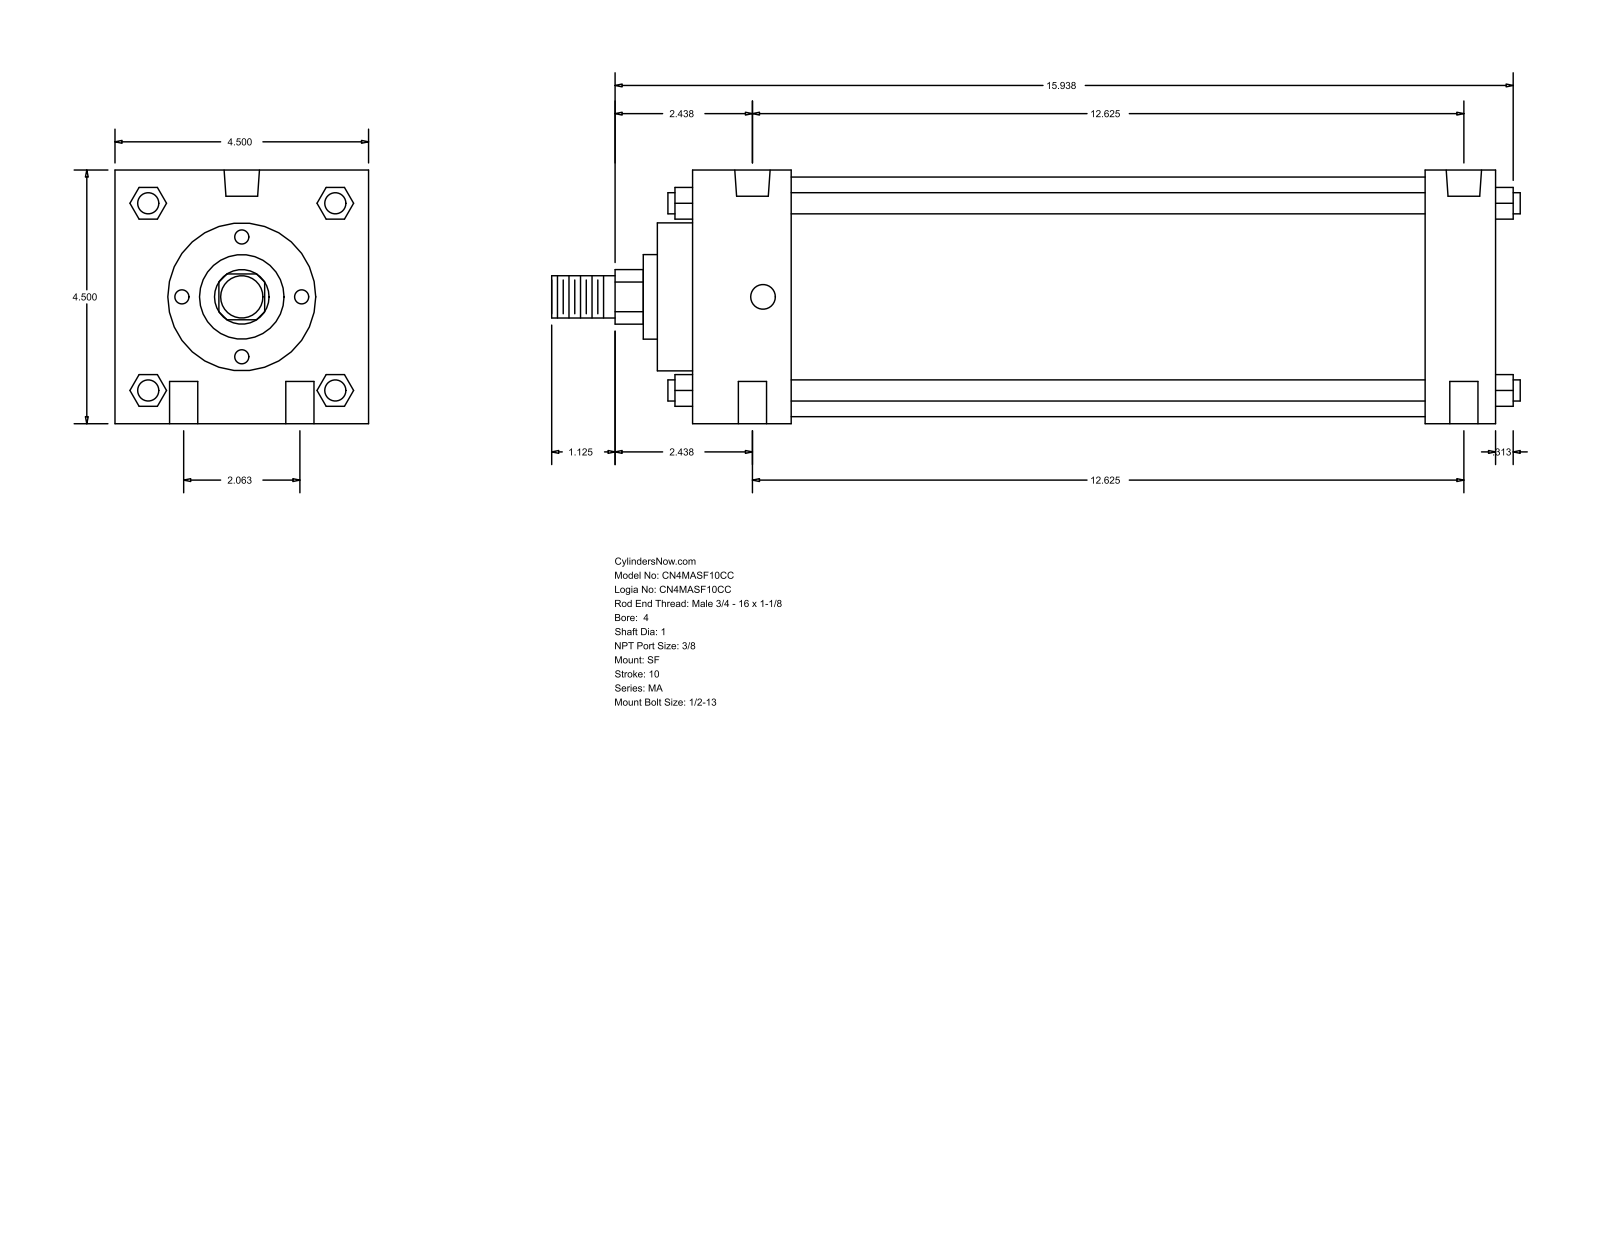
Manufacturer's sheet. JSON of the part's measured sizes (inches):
{"part_name": "MA_SF__0400_1", "step_written_by": "GSSL Pune (CONFIG_CONTROL_DESIGN)", "units": "inches", "bodies": {"solids": 0, "faces": 126, "planar": 95, "cylindrical": 31, "other": 0}, "overall_size": [17.187, 4.5, 4.5], "round_holes": [[0.5, 4], [0.437, 2], [0.627, 2]], "round_bosses_or_shafts": [[0.375, 4], [4.25, 1], [2.625, 1], [1.5, 1], [1, 1], [0.75, 1]], "partial_cylinders_radius": [[0.484, 1]], "face_to_face_distances": [4.5, 14.25, 13, 1.25, 1.75, 11.25, 12.5, 0.625, 2.375, 13.625], "hole_center_spacings": [1.031, 12.667, 12.625, 2.062, 12.793, 12.25]}
